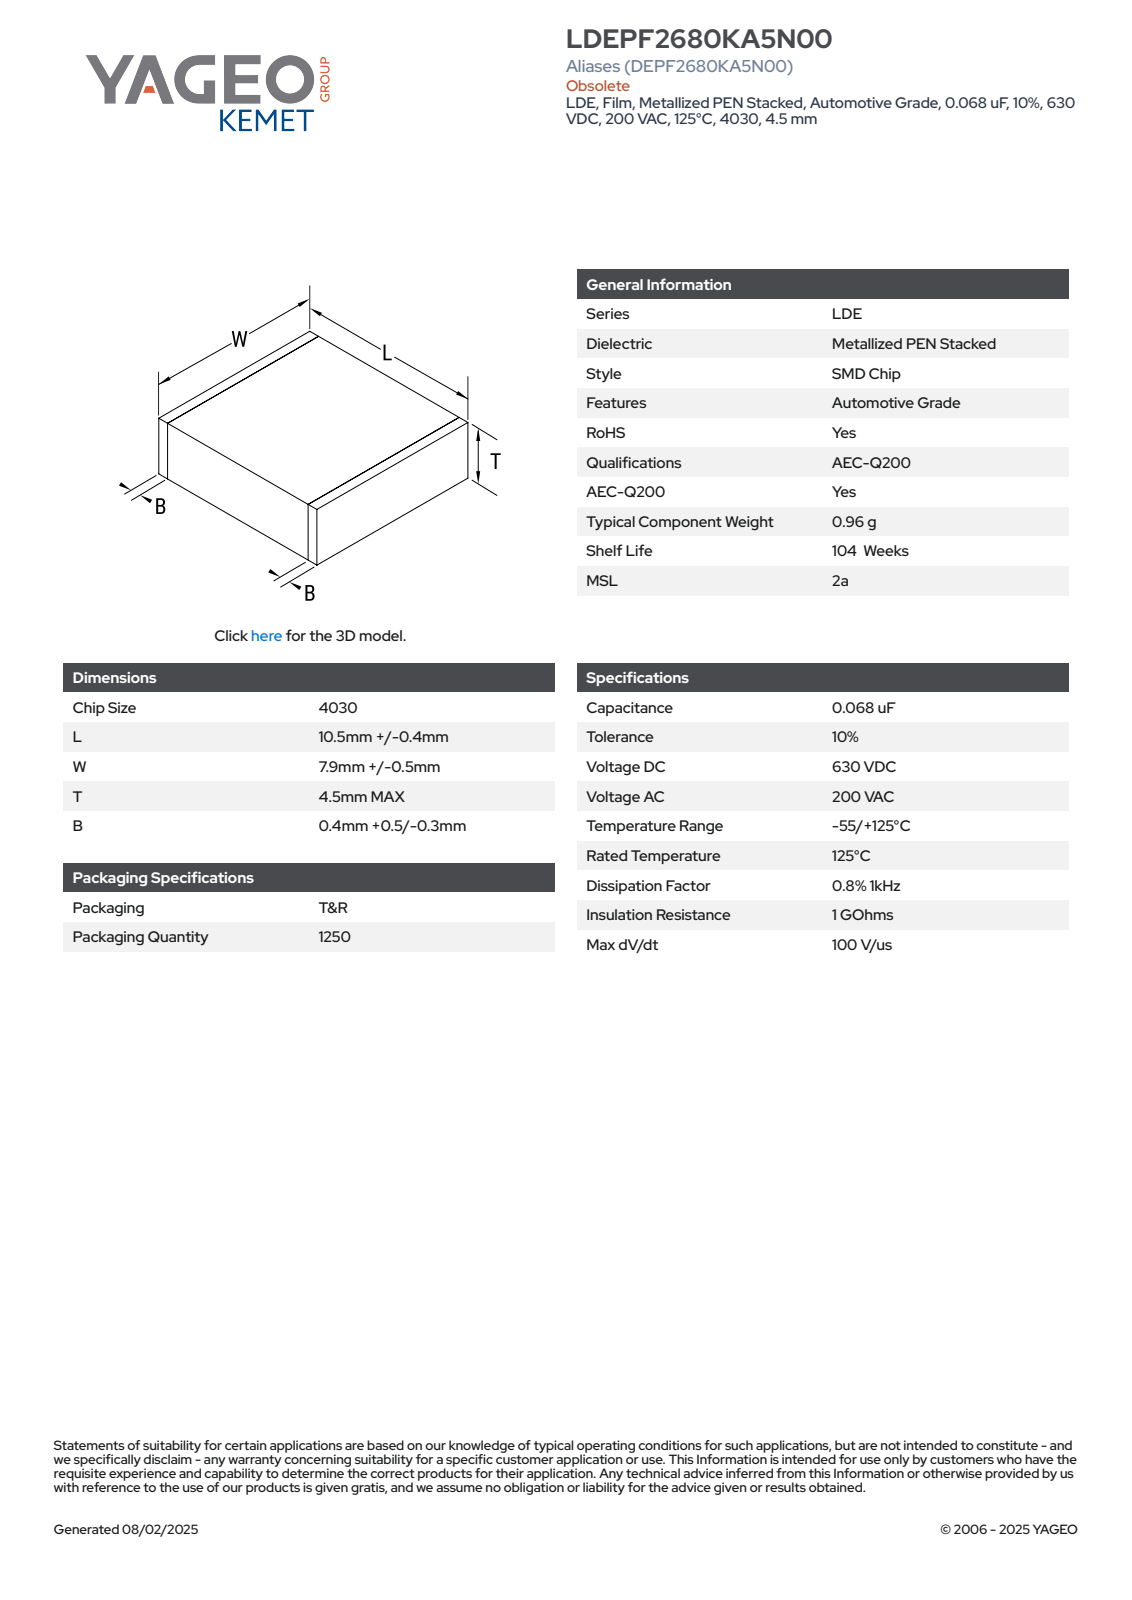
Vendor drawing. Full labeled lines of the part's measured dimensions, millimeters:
Part name (STEP PRODUCT): CFS_LDELDB_4030_L10.9W8.4T4.5B0.9
STEP written by: SolidWorks 2020 (AUTOMOTIVE_DESIGN)
Units: millimetres
Bodies: 4 solids, 73 faces (73 planar, 0 cylindrical, 0 other)
Overall size (bounding box): 10.9 × 8.4 × 4.5
Volume: 409 mm³ · Surface area: 362 mm²
Main face-to-face distances: 4.48, 8.38, 10.9, 4.49, 8.39, 4.5, 8.4, 0.5, 10.4, 9.9
